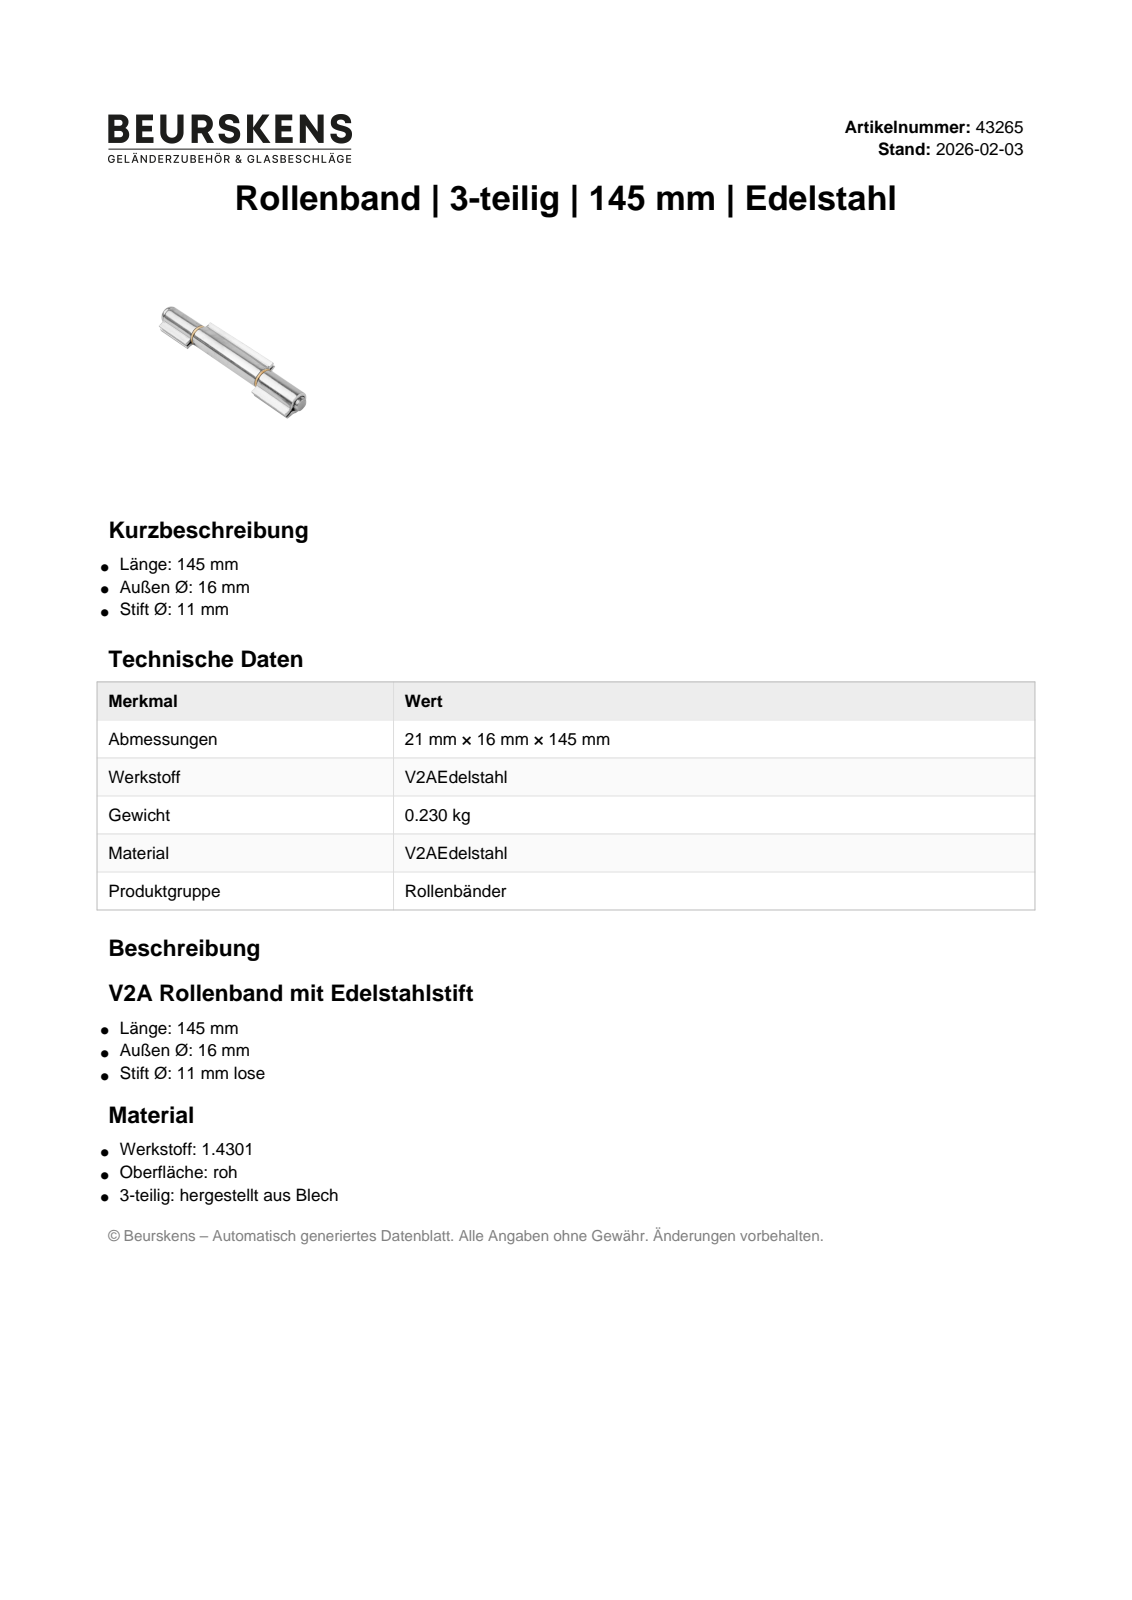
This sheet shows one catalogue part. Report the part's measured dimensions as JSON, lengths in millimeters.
{"part_name": "43265; 43265 Stift; 43265 Hülle groß; 43265 Hülle klein (+1 more)", "step_written_by": "Autodesk Inventor 2022 (AUTOMOTIVE_DESIGN)", "units": "millimeters", "bodies": {"solids": 7, "faces": 47, "planar": 33, "cylindrical": 12, "other": 2}, "overall_size": [142.5, 20.25, 16.1], "volume_mm3": 29216, "surface_area_mm2": 19987, "round_holes": [[11.1, 1]], "round_bosses_or_shafts": [[16.1, 1], [16, 1]], "face_to_face_distances": [1.03, 68.25, 2, 33, 101.25, 103.25, 35, 1.67, 2.7, 4.38]}
